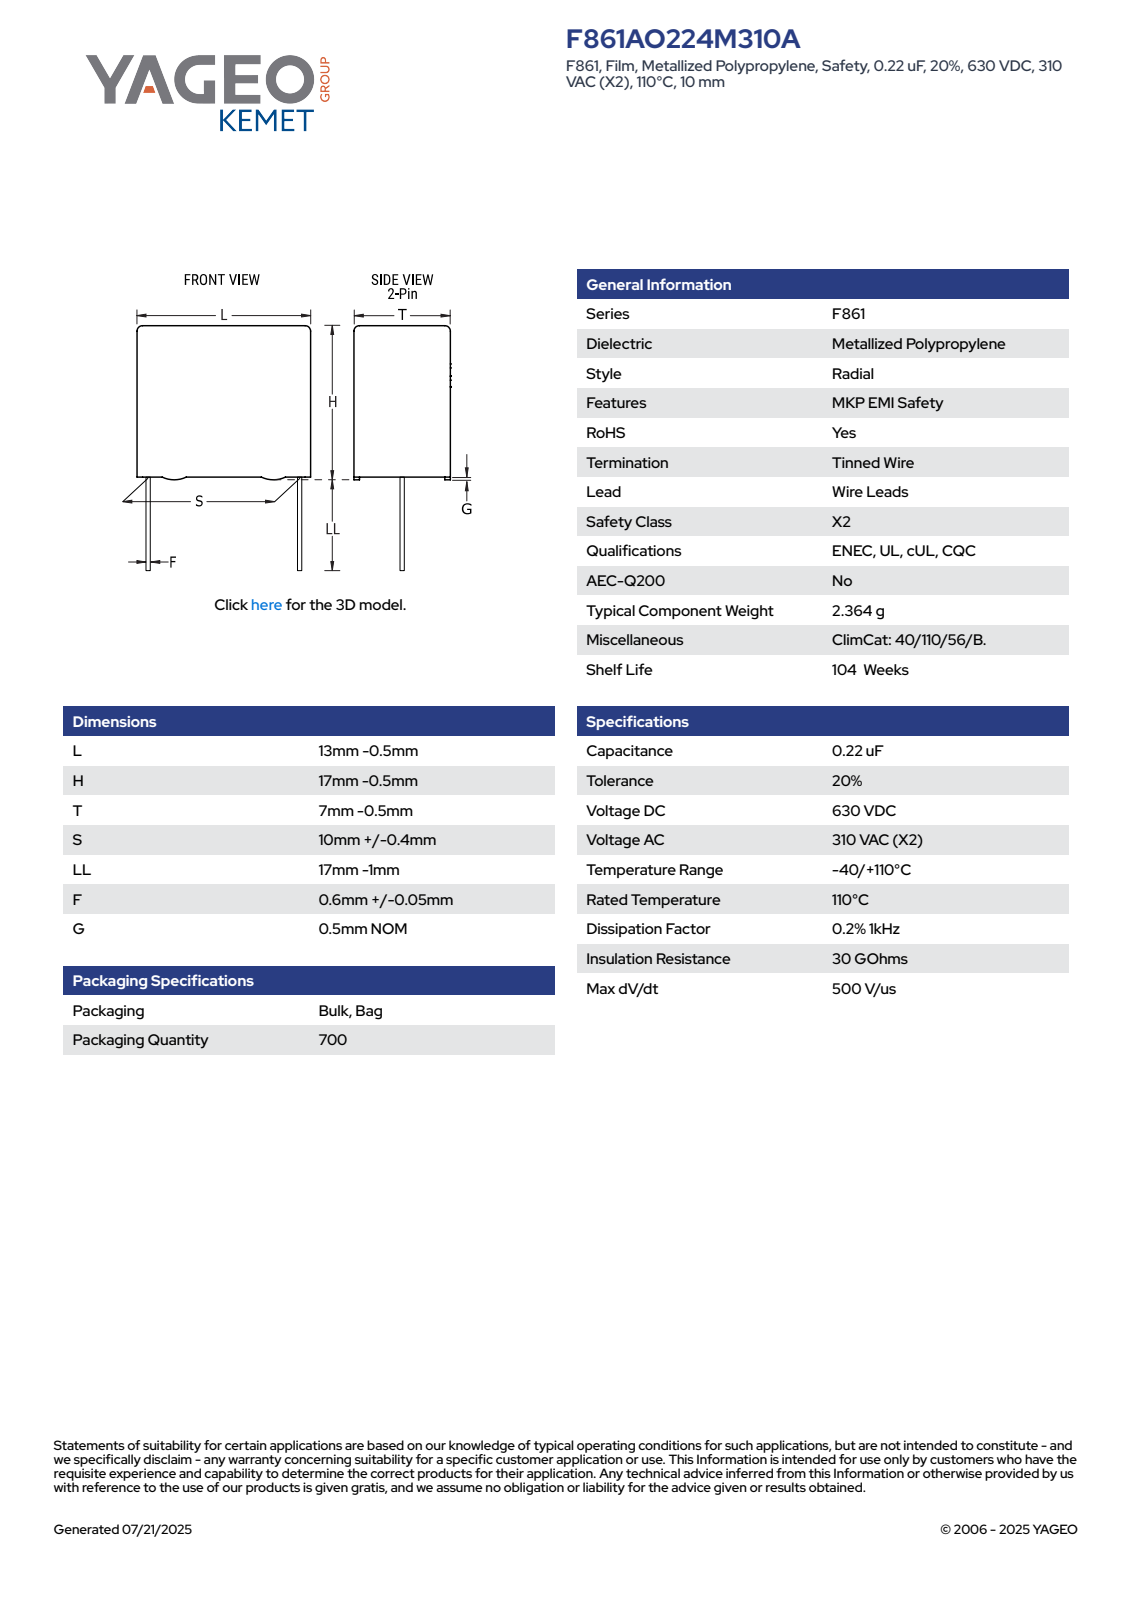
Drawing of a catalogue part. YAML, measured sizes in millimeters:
part_name: "CFR_RBG_13X17X7_L12.5H16.5T6.5S10LL16F0.65G0.5"
step_written_by: "SolidWorks 2014 (AUTOMOTIVE_DESIGN)"
units: millimeters
bodies: {solids: 4, faces: 89, planar: 81, cylindrical: 8, other: 0}
overall_size: [32.5, 12.5, 6.5]
volume: 1311
surface_area: 856
round_bosses_or_shafts:
  - {diameter: 0.65, count: 2}
partial_cylinders:
  - {radius: 0.5, count: 4}
face_to_face_distances: [6.5, 12.5, 16, 0.37, 6.13, 16.5, 0.5, 5.76, 32.5, 5.54]
